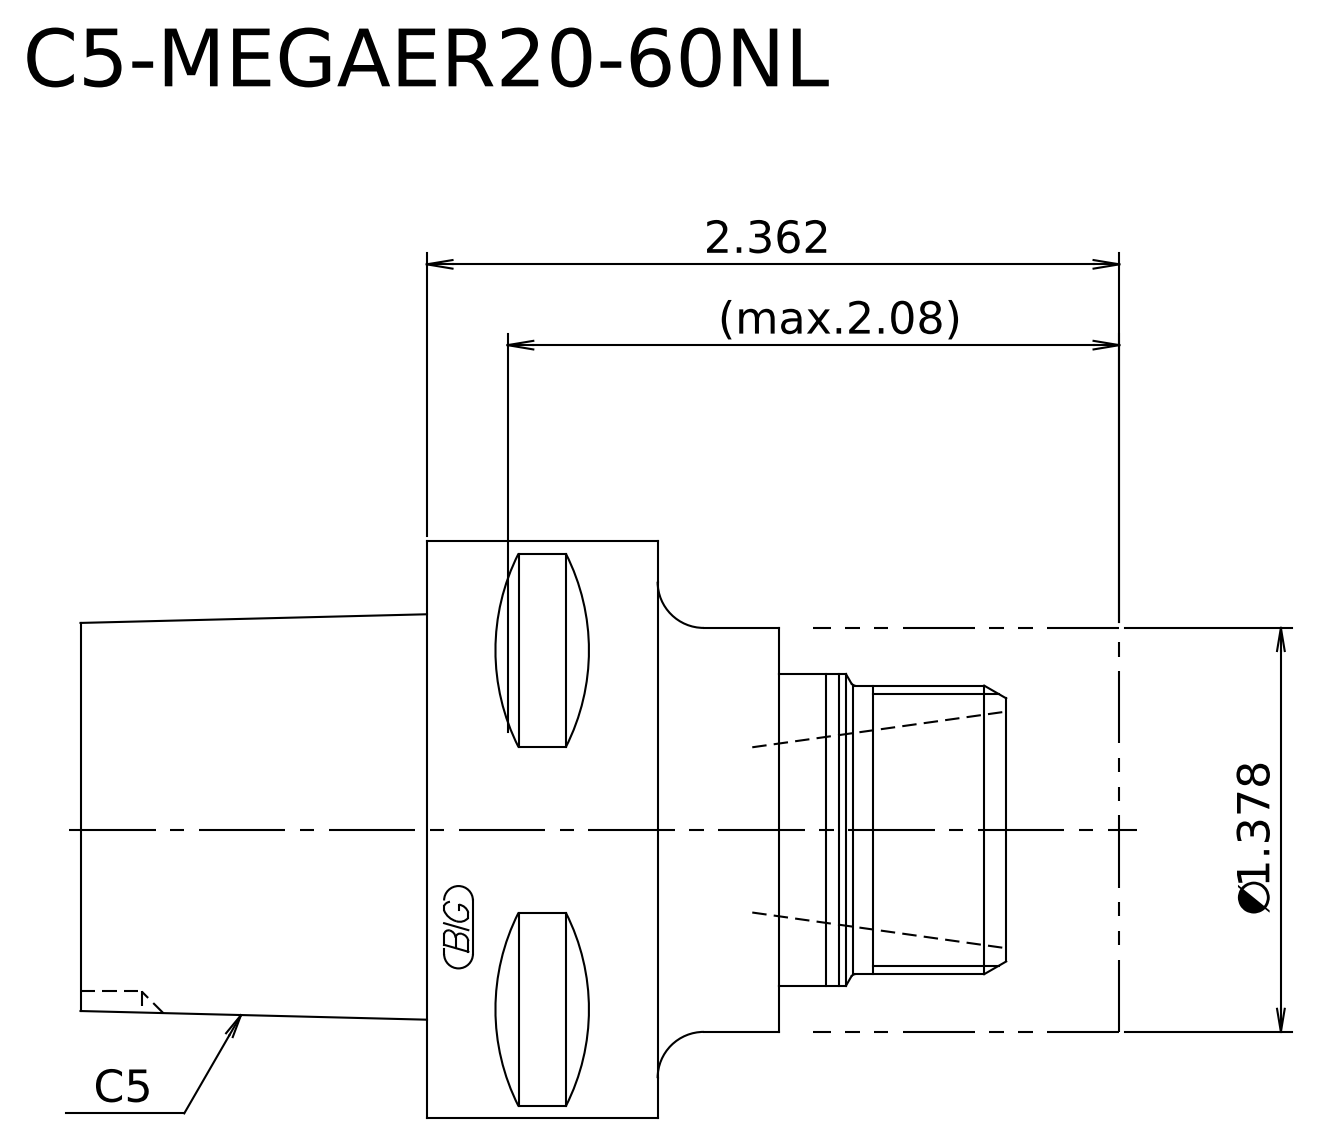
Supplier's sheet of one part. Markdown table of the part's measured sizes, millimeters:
| quantity | value |
| --- | --- |
| STEP written by | Kubotek KeyCreator 2011 V10.0.2 (22737) (automotive_design) |
| units | millimeters |
| bodies | 2 solids, 16 faces (7 planar, 5 cylindrical, 4 other) |
| overall size | 90 × 50 × 50 |
| volume | 113 103 mm³ |
| surface area | 17 470 mm² |
| round bosses / shafts (diameter × count) | 50 × 1, 35 × 1, 27 × 1, 25 × 1 |
| main face-to-face distances | 33.5, 26.5, 60, 90, 63.5, 30, 40, 13.5, 20, 50 |
